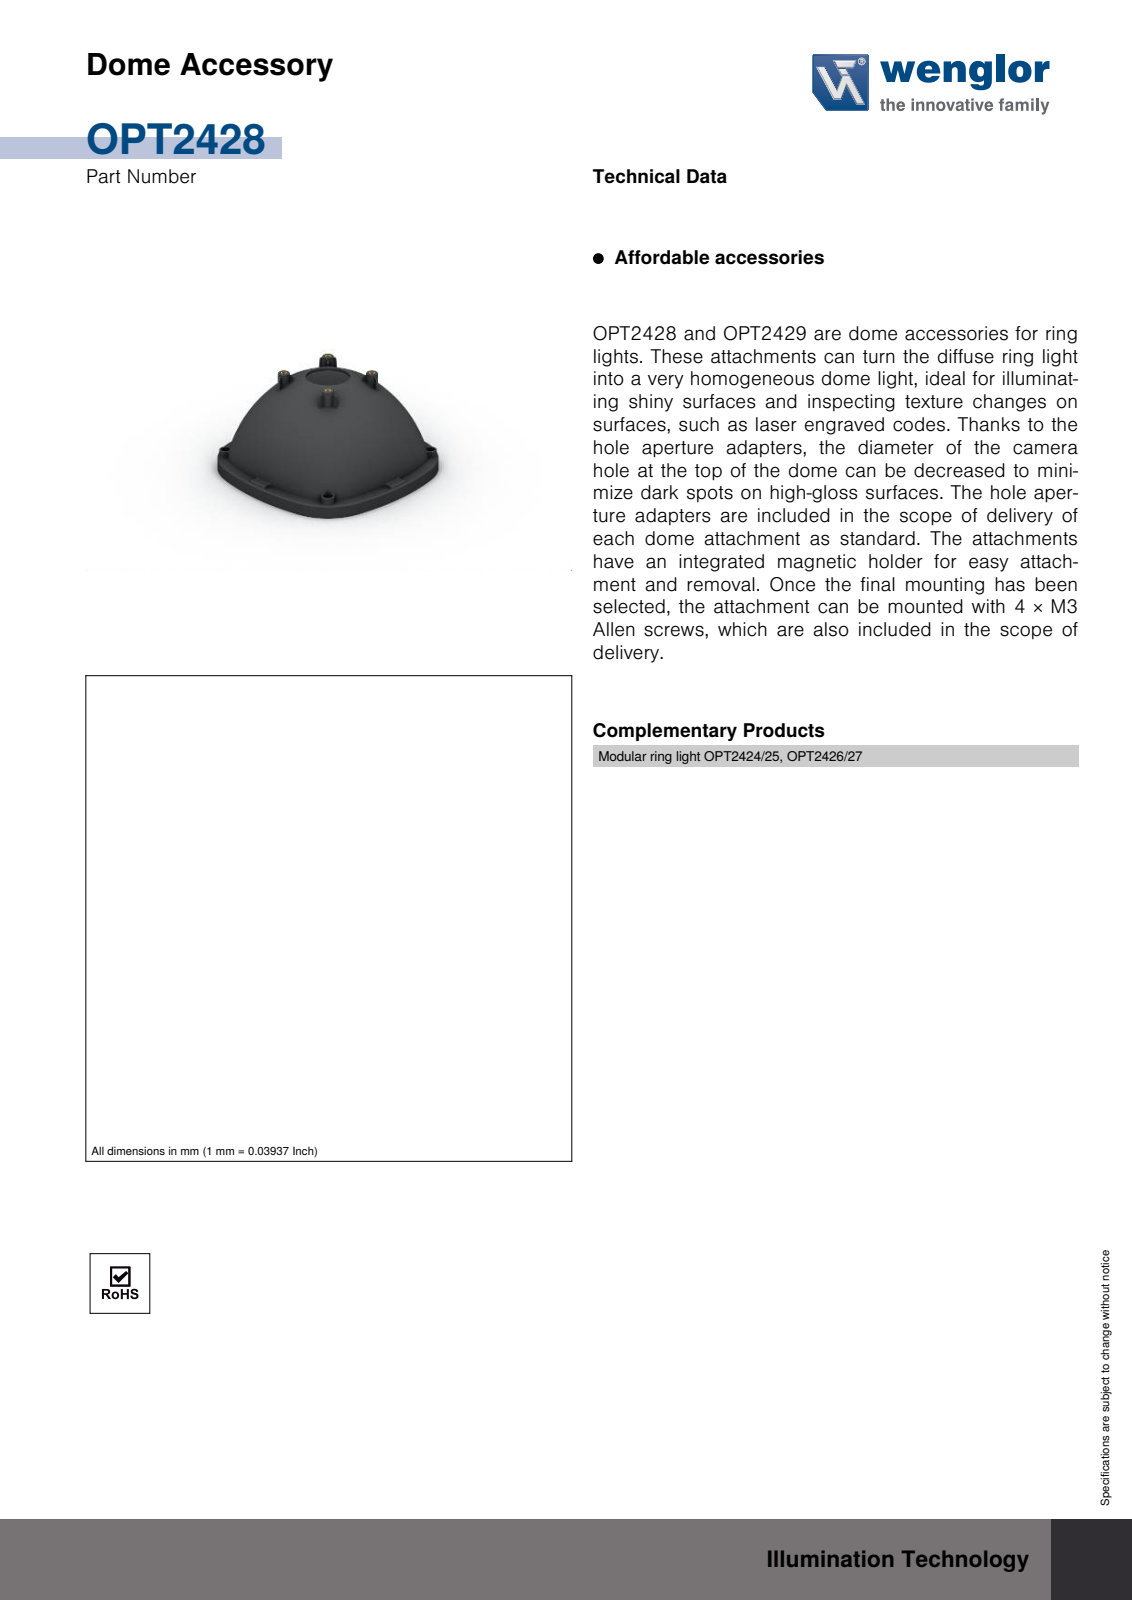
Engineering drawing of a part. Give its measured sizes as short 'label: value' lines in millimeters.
name: OPT2428
written by: SolidWorks 2021 (AUTOMOTIVE_DESIGN)
unit: mm
bodies: 1 solid, 1088 faces (146 planar, 235 cylindrical, 707 other)
size: 136 × 134 × 71.1
volume: 61 990 mm³; area: 61 760 mm²
holes: 4× ⌀3, 4× ⌀3.4, 4× ⌀4.2, 1× ⌀30
rounds: 96× R0.3, 29× R1, 16× R0.5, 14× R0.2, 12× R2, 4× R28, 4× R150.1
face distances: 2, 6.8, 8.7, 10.7, 4, 64, 62, 2, 4.5, 124.1
hole spacings: 42, 76.3, 76.3, 100, 59.4, 29.7, 40.6, 99.4
